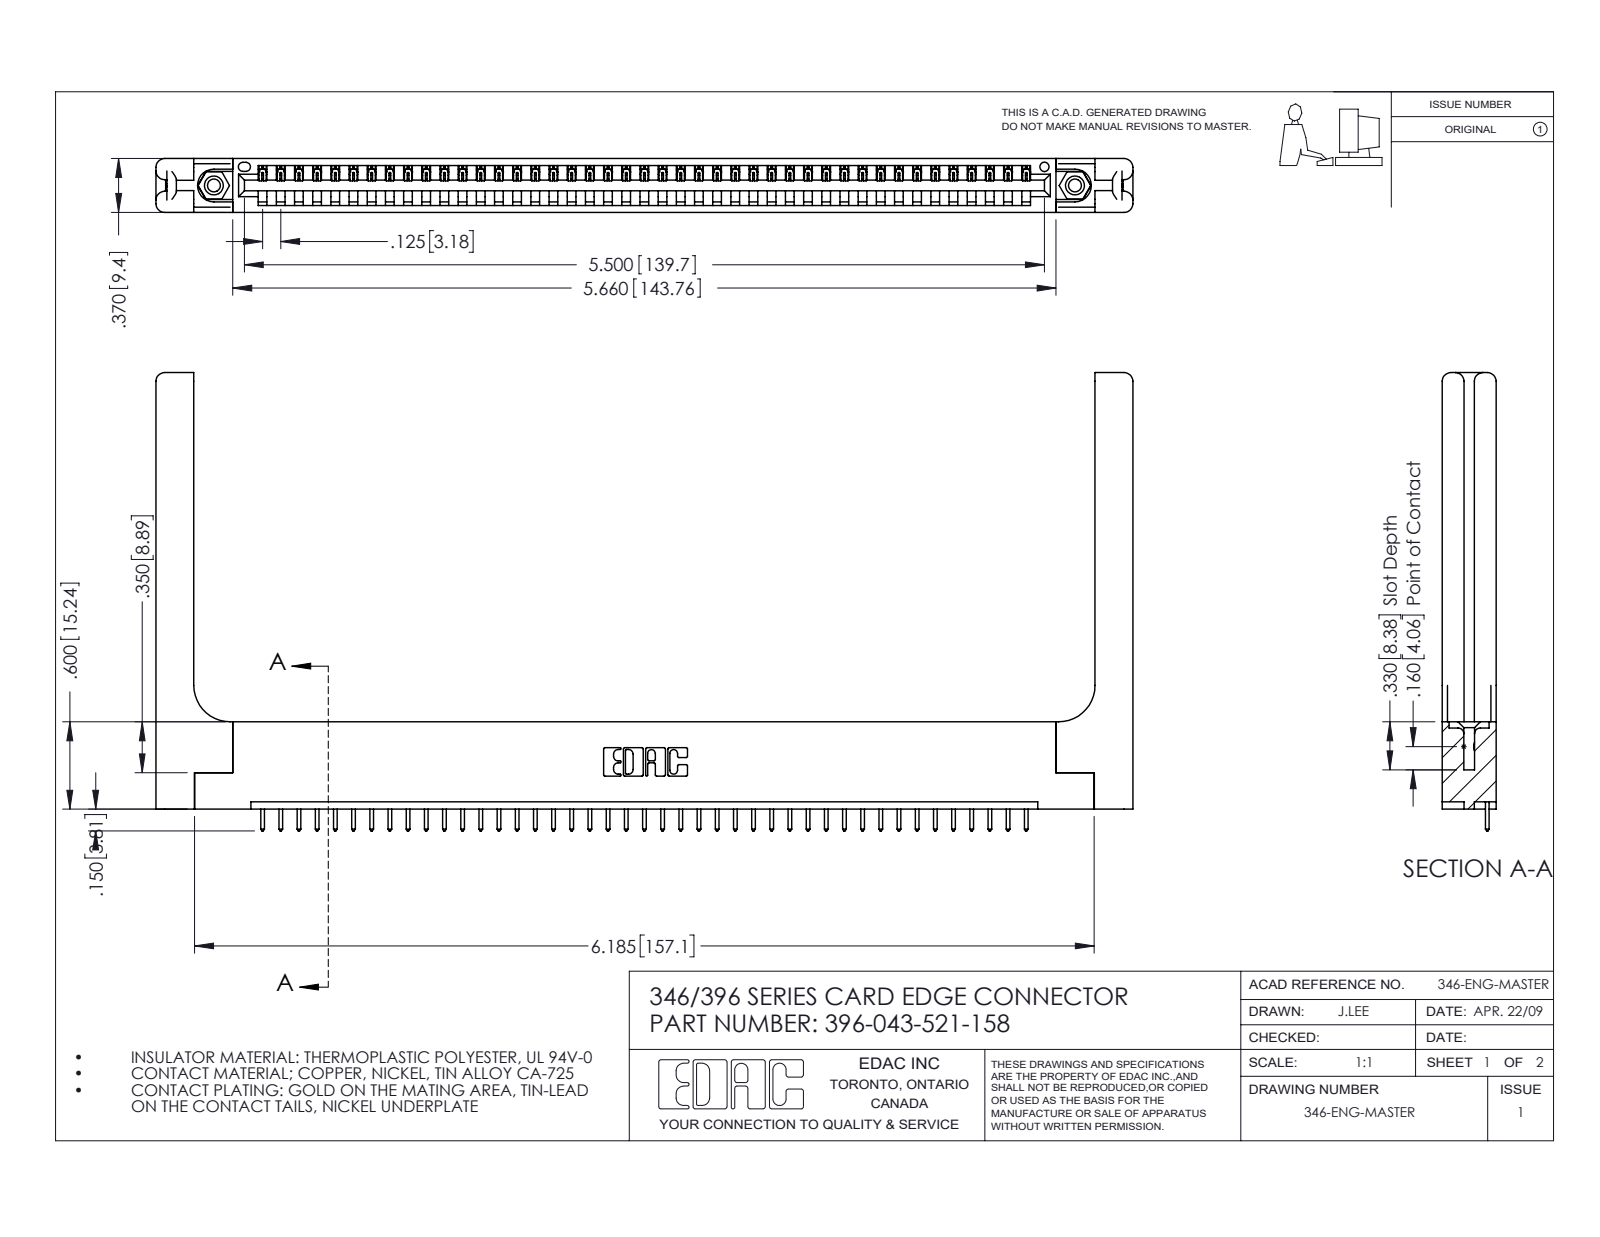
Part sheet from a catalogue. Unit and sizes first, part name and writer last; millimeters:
Units: millimetres
Overall size (bounding box): 170.6 × 80 × 9.4
Round holes (diameter × count): ⌀2.3 ×2, ⌀3.2 ×2, ⌀4 ×2, ⌀1.6 ×1
Round bosses / shafts (diameter × count): ⌀3.9 ×2
Partial cylindrical surfaces — rounded edges, fillets, slot ends (radius × count): R0.2 ×86, R0.3 ×86, R0.3 ×22, R1.5 ×16, R0.2 ×6, R0.8 ×6, R0.7 ×3, R0.8 ×2
Main face-to-face distances: 9.4, 1.2, 8.2, 1.8, 3.8, 3.8, 6.4, 7.6, 0.6, 5.6
Hole centre spacings: 6.2, 145.1, 150.4
Volume: 23 730 mm³ · Surface area: 24 960 mm²
Bodies: 48 solids, 2872 faces (1944 planar, 868 cylindrical, 60 other)
Part name (STEP PRODUCT): 345-292-001_345-293-121; 346 Part_Flush Mounting Lugs - 0.156 Dia-TH; 346-220-058_345-220-058; 345-250-001_345-250-001-102 (+1 more)
STEP written by: SolidWorks 2016 (CONFIG_CONTROL_DESIGN)
